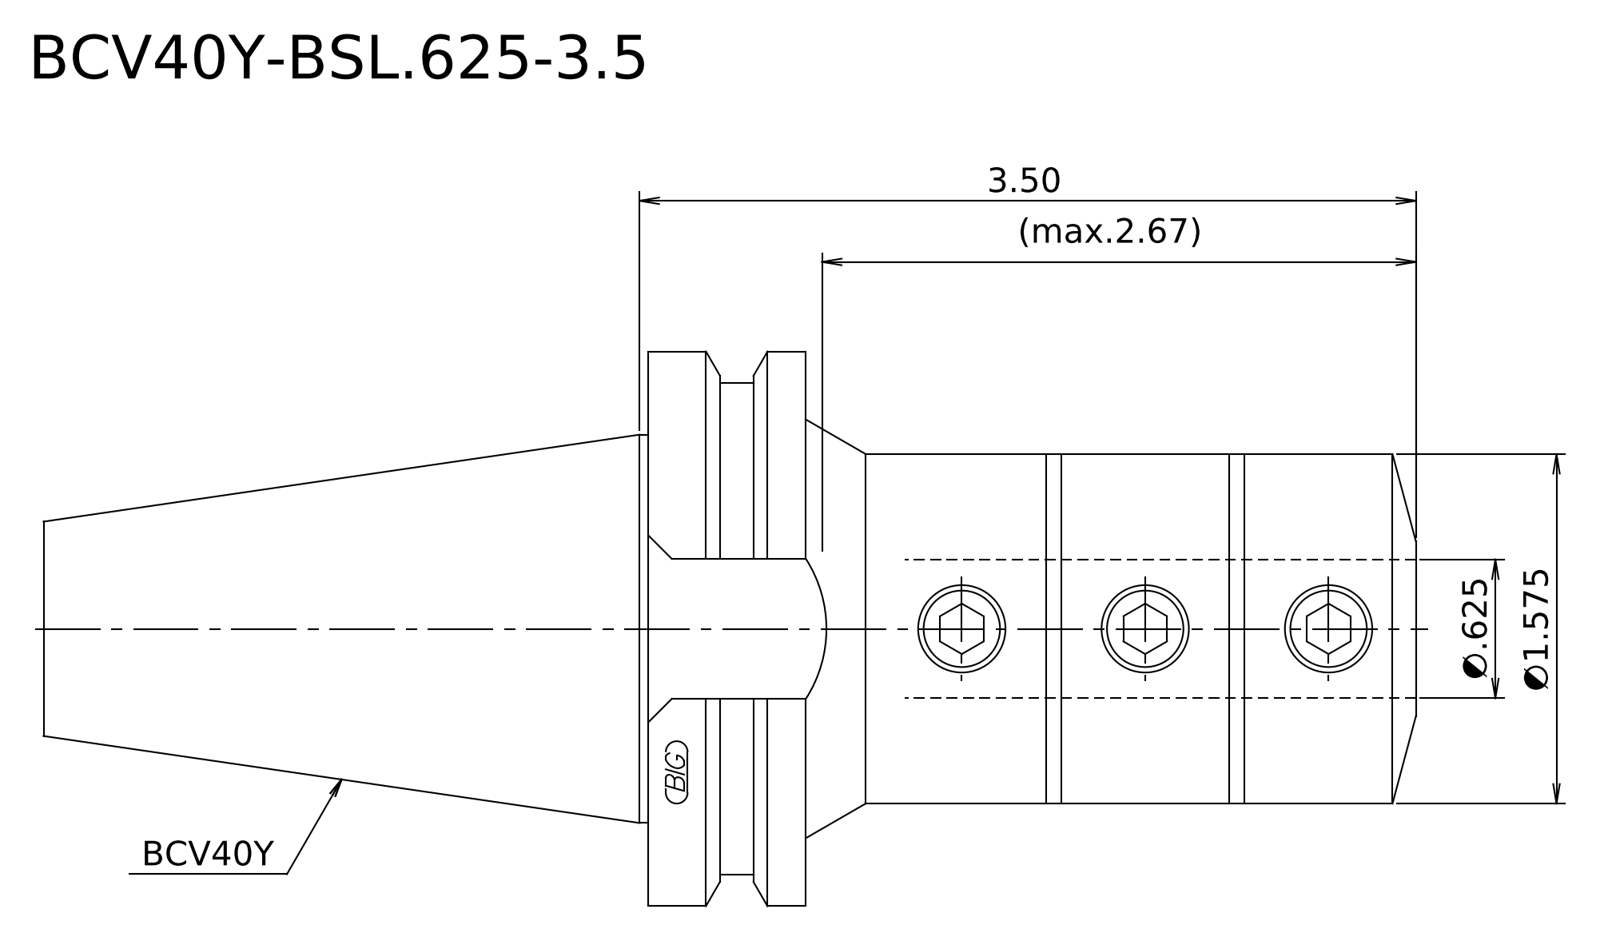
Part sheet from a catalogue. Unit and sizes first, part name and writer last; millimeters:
Units: millimetres
Overall size (bounding box): 157.15 × 63.5 × 63.5
Round bosses / shafts (diameter × count): ⌀63.5 ×1, ⌀56.36 ×1, ⌀44.45 ×1, ⌀40 ×1
Main face-to-face distances: 18.05, 87.3, 69.25, 69.85, 87.9, 157.15, 79.7, 9.85, 8.2, 77.45
Volume: 209 016 mm³ · Surface area: 25 411 mm²
Bodies: 1 solid, 16 faces (6 planar, 5 cylindrical, 5 other)
STEP written by: Kubotek KeyCreator 2011 V10.0.2 (22737) (automotive_design)
